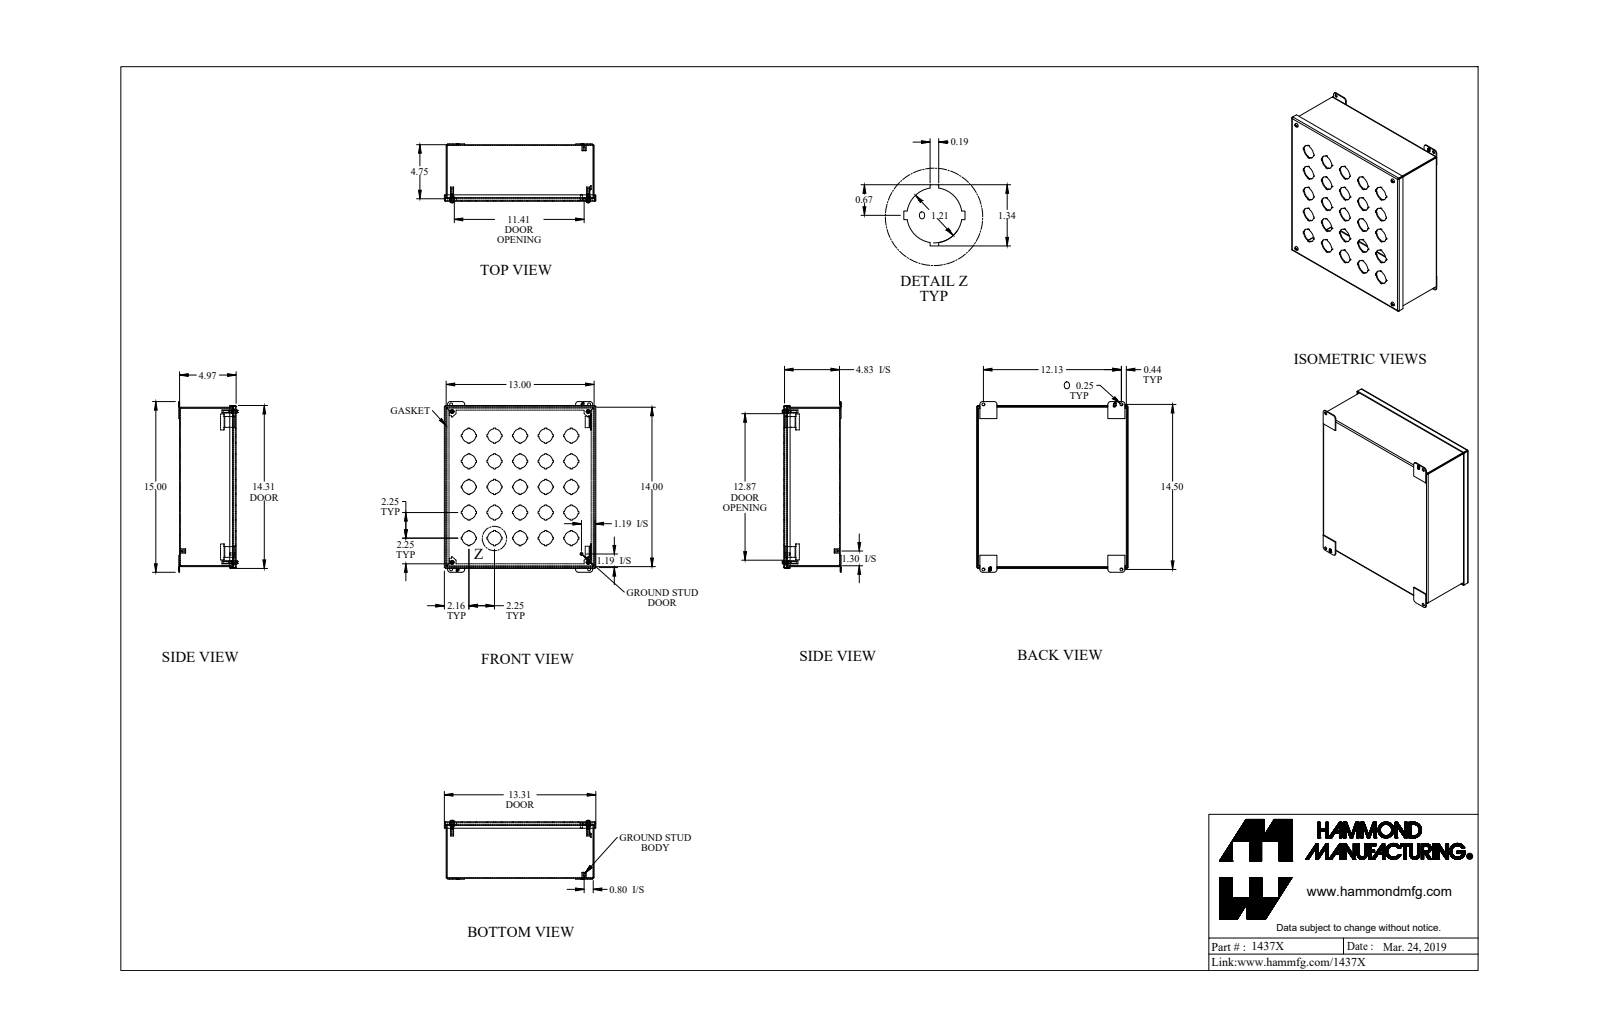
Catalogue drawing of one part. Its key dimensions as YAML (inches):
part_name: "1437X_Default"
step_written_by: "SolidWorks 2019 (CONFIG_CONTROL_DESIGN)"
units: inches
bodies: {solids: 23, faces: 1115, planar: 799, cylindrical: 260, other: 56}
overall_size: [15, 13.312, 5.171]
volume: 51.21
surface_area: 1376
round_holes:
  - {diameter: 1.21, count: 25}
  - {diameter: 0.25, count: 8}
  - {diameter: 0.159, count: 4}
  - {diameter: 0.406, count: 4}
  - {diameter: 0.156, count: 1}
round_bosses_or_shafts:
  - {diameter: 0.39, count: 4}
  - {diameter: 0.275, count: 4}
  - {diameter: 0.19, count: 4}
  - {diameter: 0.148, count: 4}
  - {diameter: 0.375, count: 1}
  - {diameter: 0.25, count: 1}
  - {diameter: 0.188, count: 1}
partial_cylinders:
  - {radius: 0.036, count: 12}
  - {radius: 0.108, count: 12}
  - {radius: 0.25, count: 8}
  - {radius: 0.029, count: 4}
  - {radius: 0.086, count: 4}
  - {radius: 0.16, count: 4}
  - {radius: 0.171, count: 4}
  - {radius: 0.125, count: 2}
face_to_face_distances: [0.072, 4.9, 4.828, 4.972, 12.928, 13.928, 13, 12.856, 14, 13.856]
hole_center_spacings: [2.25, 5.031, 3.182, 4.5, 7.115, 0.63, 6.364, 6.75]
